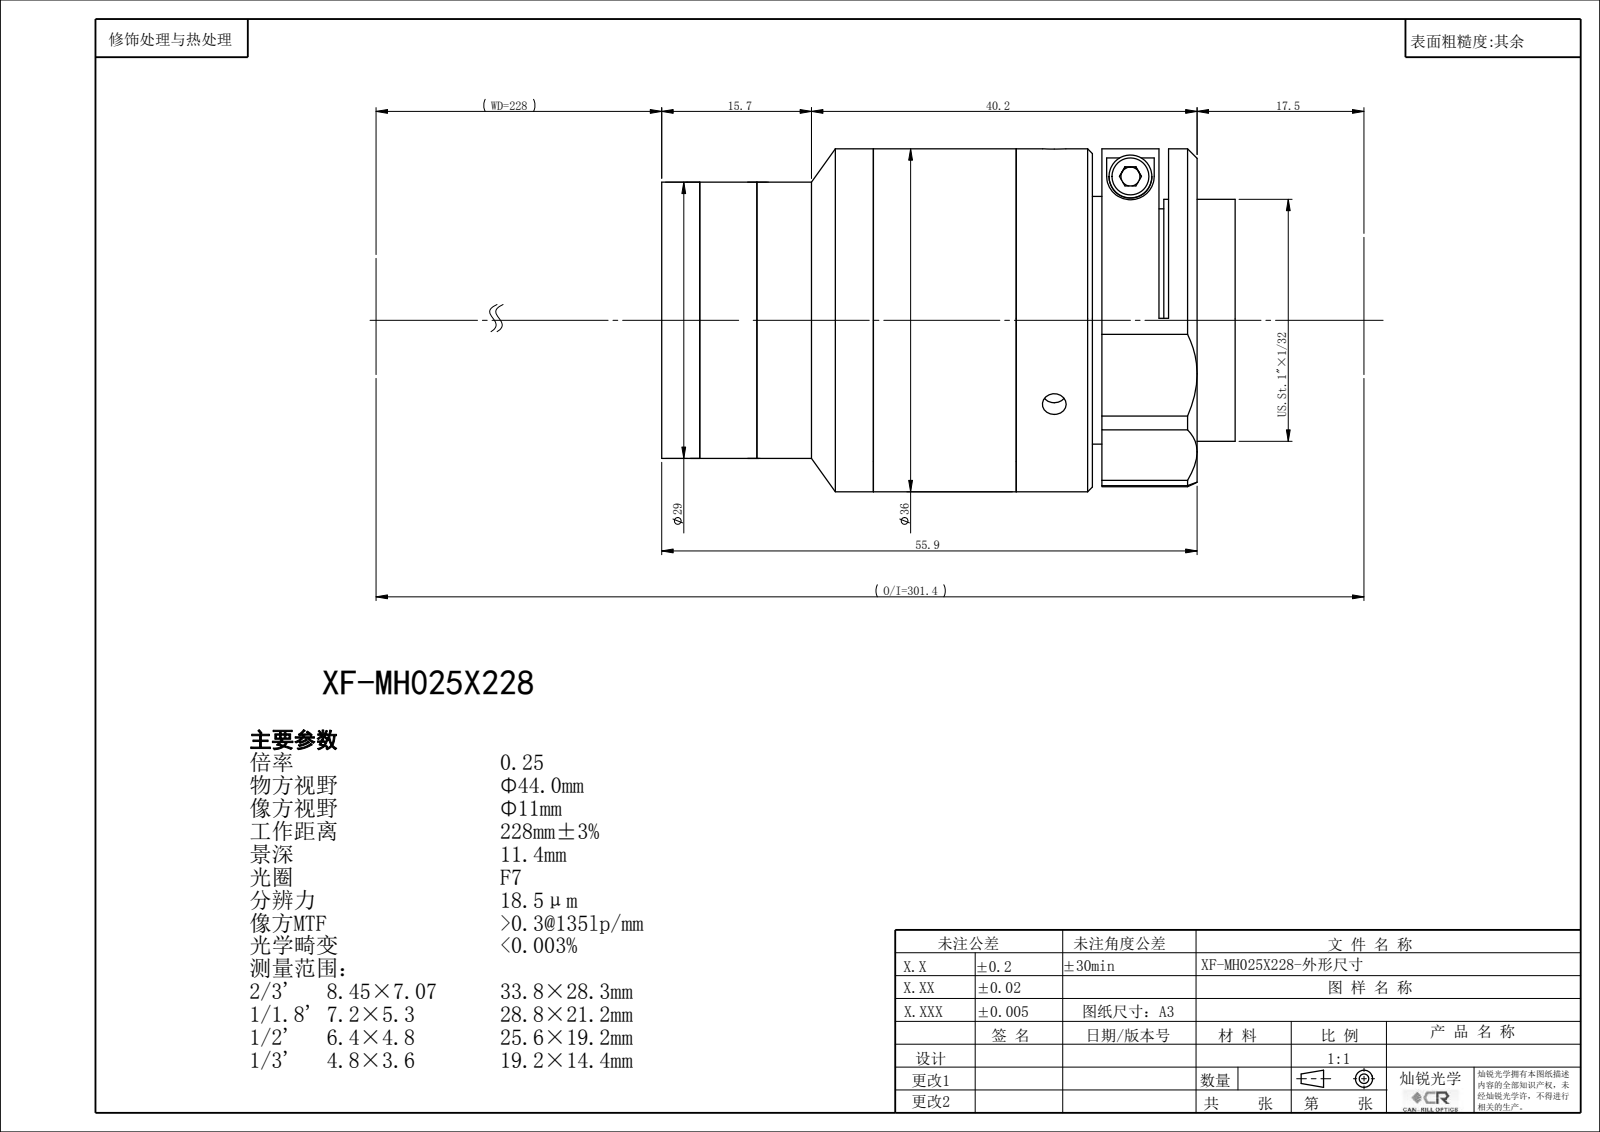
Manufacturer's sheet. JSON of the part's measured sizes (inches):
{"part_name": "XF-MH025X228", "step_written_by": "SolidWorks 2022 (CONFIG_CONTROL_DESIGN)", "units": "inches", "bodies": {"solids": 0, "faces": 124, "planar": 62, "cylindrical": 46, "other": 16}, "overall_size": [2.385, 1.417, 1.417], "round_holes": [[0.098, 6], [0.551, 1], [0.882, 1], [0.945, 1], [0.98, 1], [1.024, 1], [1.039, 1]], "round_bosses_or_shafts": [[1.417, 1], [1.339, 1], [1.142, 1], [1, 1]], "face_to_face_distances": [0.761, 1.317, 2.078, 0.059, 2.019, 0.702, 0.726, 0.591, 1.293, 1.352], "hole_center_spacings": [0.374]}
